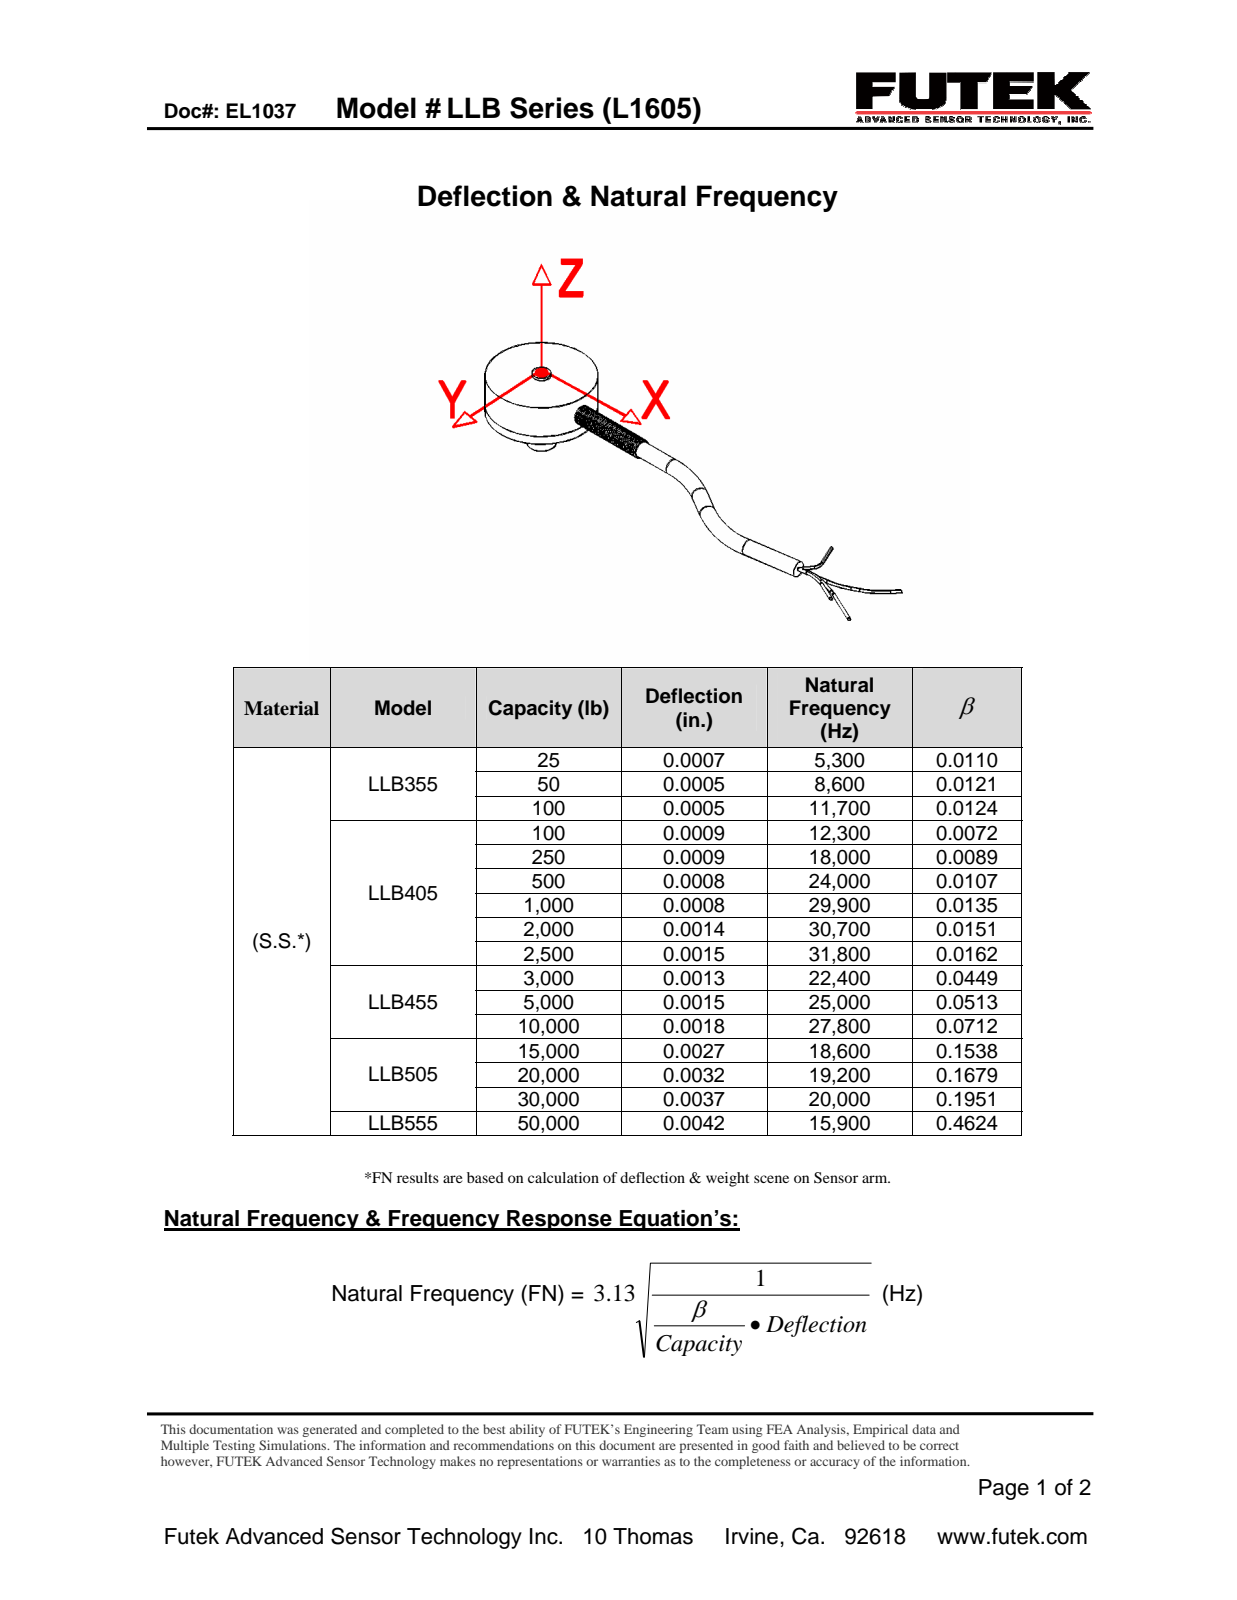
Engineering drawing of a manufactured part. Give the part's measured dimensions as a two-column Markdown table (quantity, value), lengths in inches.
| quantity | value |
| --- | --- |
| part name | LLB555 (LevelofDetail1); ~~~~PART1 (~1); 778C; 778CA (+1 more) |
| STEP written by | Autodesk Inventor 2008 (AUTOMOTIVE_DESIGN) |
| units | inches |
| bodies | 3 solids, 243 faces (93 planar, 55 cylindrical, 95 other) |
| overall size | 6.619 × 2.98 × 2.25 |
| volume | 11.12 in³ |
| surface area | 34.4 in² |
| round holes (diameter × count) | 0.242 × 3, 0.13 × 1, 0.155 × 1, 0.178 × 1, 0.189 × 1, 0.21 × 1, 0.219 × 1, 0.228 × 1, 1.77 × 1 |
| round bosses / shafts (diameter × count) | 0.226 × 3, 0.125 × 3, 2.98 × 1, 0.78 × 1, 0.5 × 1, 0.46 × 1, 0.278 × 1, 0.225 × 1 |
| partial cylindrical surfaces (radius × count) | 0.083 × 1, 0.097 × 1 |
| main face-to-face distances | 1.57, 0.02, 1.55, 0.5, 2.05, 2.07, 0.51, 1.54, 1.56, 0.109 |
| hole center spacings | 1.187, 2.057 |
